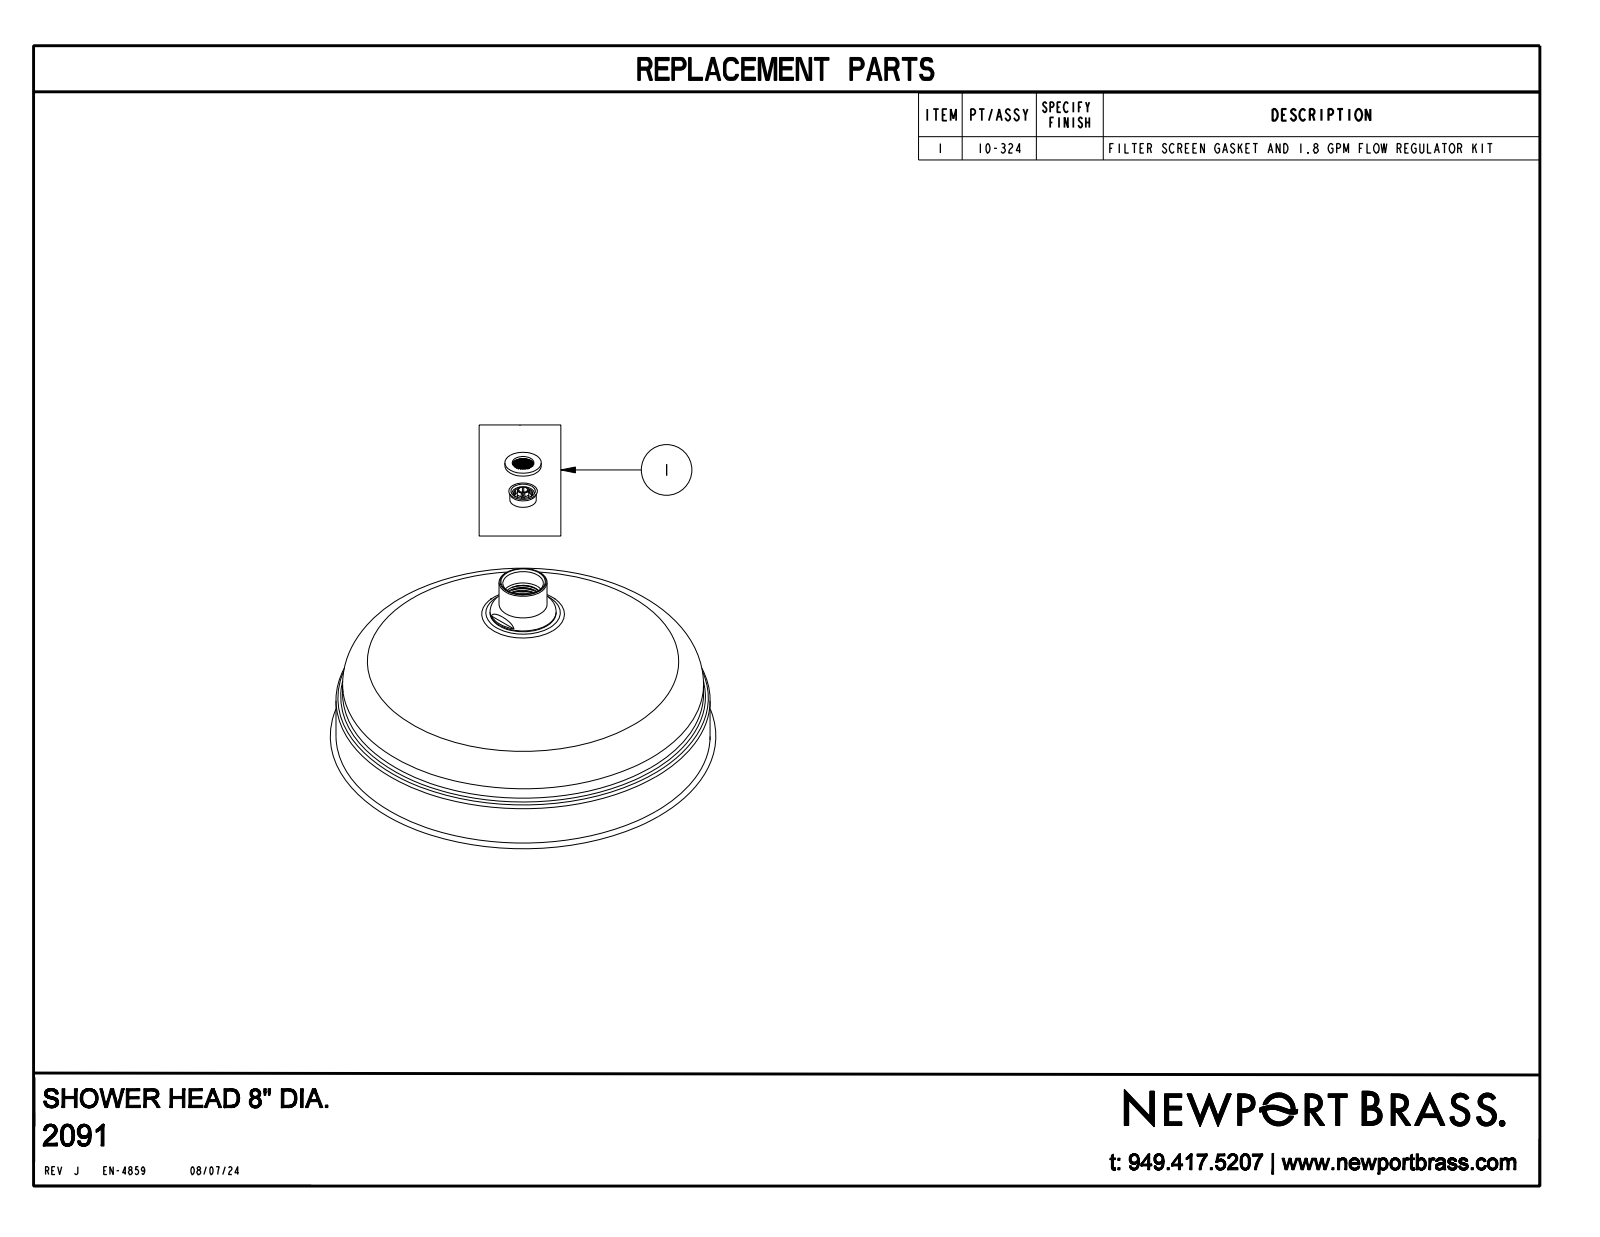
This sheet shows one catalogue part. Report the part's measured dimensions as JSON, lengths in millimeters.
{"part_name": "11947_AF0; 11943_AF0; 11948_AF0; 2091A_AF0_ASM (+1 more)", "step_written_by": "CREO PARAMETRIC BY PTC INC, 2018400 (AUTOMOTIVE_DESIGN)", "units": "millimeters", "bodies": {"solids": 3, "faces": 1224, "planar": 16, "cylindrical": 304, "other": 904}, "overall_size": [204, 204, 101.6], "volume_mm3": 61420, "surface_area_mm2": 197000, "round_holes": [[1, 141], [28, 1], [184.6, 1], [190, 1], [197, 1]], "round_bosses_or_shafts": [[198, 1], [191, 1], [186, 1], [34.9, 1], [27.9, 1], [25.4, 1], [20.8, 1]], "face_to_face_distances": [0.5, 1.2, 1.7, 0.7, 64.1, 62.9, 64.6, 63.4, 63.6, 62.4], "hole_center_spacings": [72, 29.9, 44.5, 96.4, 140.9, 15.1, 58.6, 84.6]}
